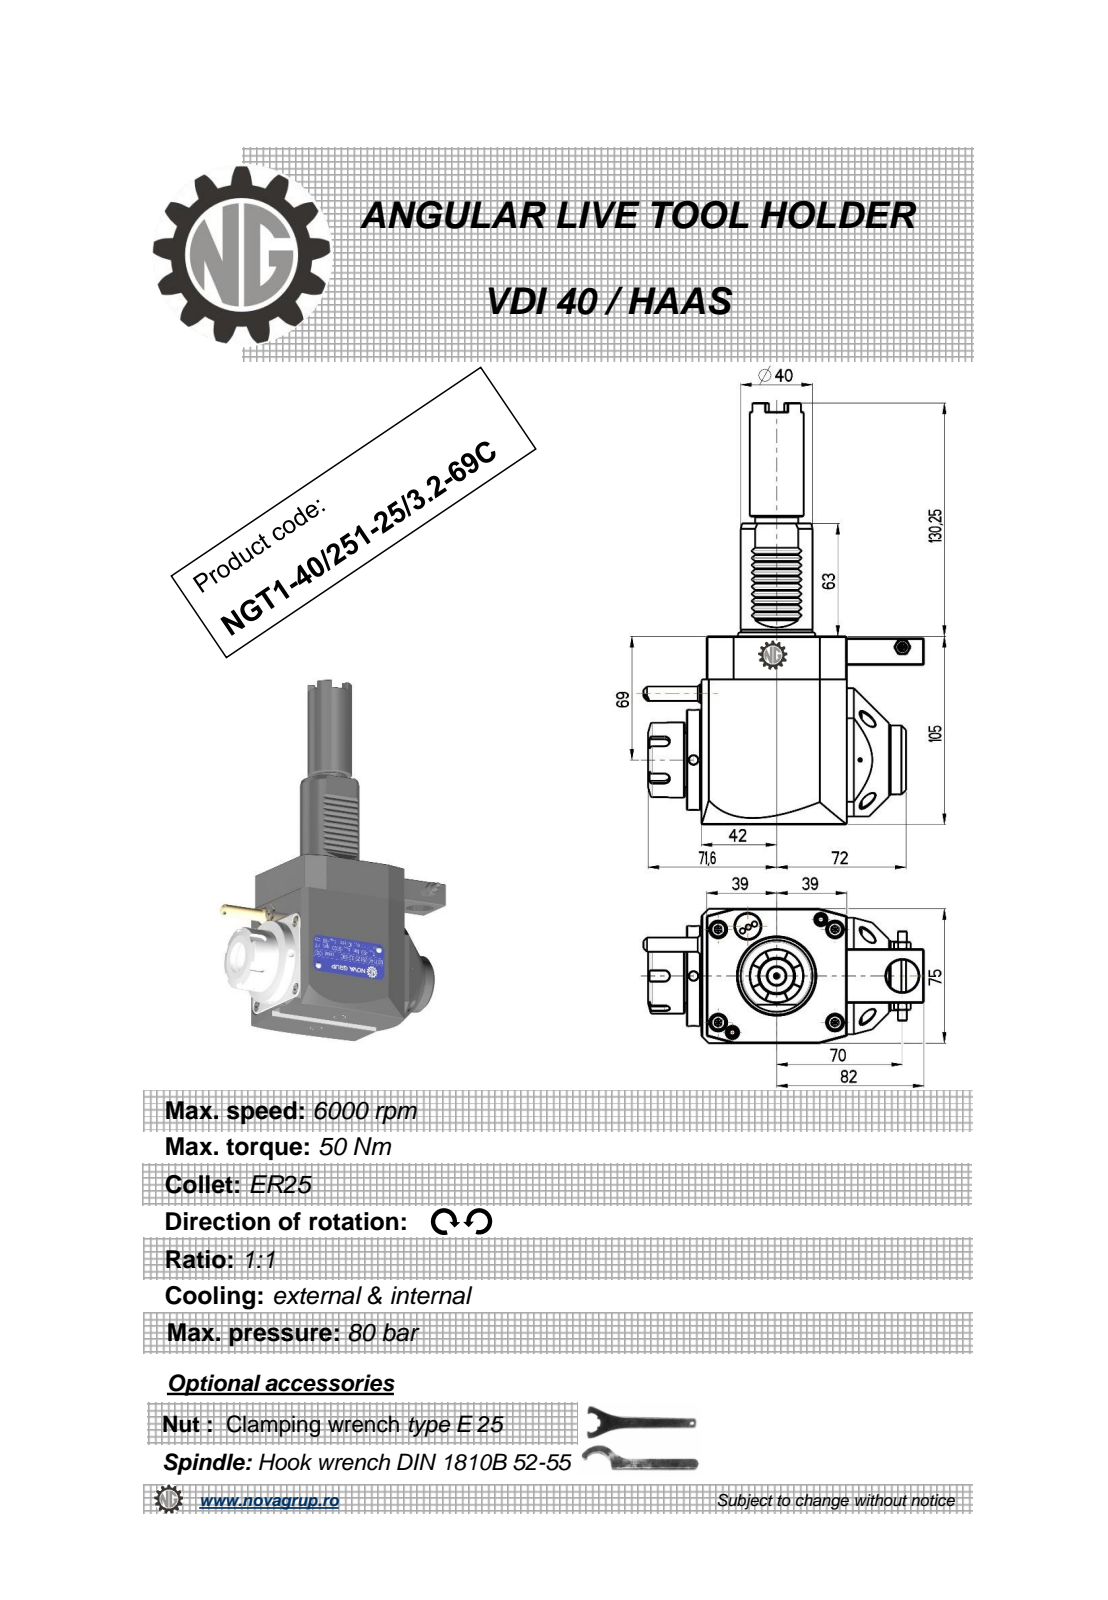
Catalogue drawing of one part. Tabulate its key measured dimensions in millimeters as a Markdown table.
| quantity | value |
| --- | --- |
| part name | NGT1_40_251_25_3_2_69C |
| STEP written by | PRO/ENGINEER BY PARAMETRIC TECHNOLOGY CORPORATION, 2010280 (CONFIG_CONTROL_DESIGN) |
| units | millimeters |
| bodies | 1 solid, 471 faces (220 planar, 89 cylindrical, 162 other) |
| overall size | 235.25 × 156.14 × 75 |
| volume | 876 662 mm³ |
| surface area | 77 536 mm² |
| round holes (diameter × count) | 5 × 3, 3 × 1, 4.2 × 1, 9.5 × 1, 18 × 1, 20 × 1, 20.3 × 1 |
| round bosses / shafts (diameter × count) | 56 × 1, 43 × 1, 42 × 1, 40 × 1, 38.5 × 1, 33 × 1, 30 × 1, 24 × 1 |
| partial cylindrical surfaces (radius × count) | 0.26 × 12, 0.3 × 10, 0.2 × 6, 3 × 5, 0.5 × 1, 40 × 1 |
| main face-to-face distances | 75, 105, 89, 81, 8, 11, 1, 3, 2.8, 78 |
| hole center spacings | 30.11, 40.93, 46.25, 61.5, 70, 116.25, 132.22 |
